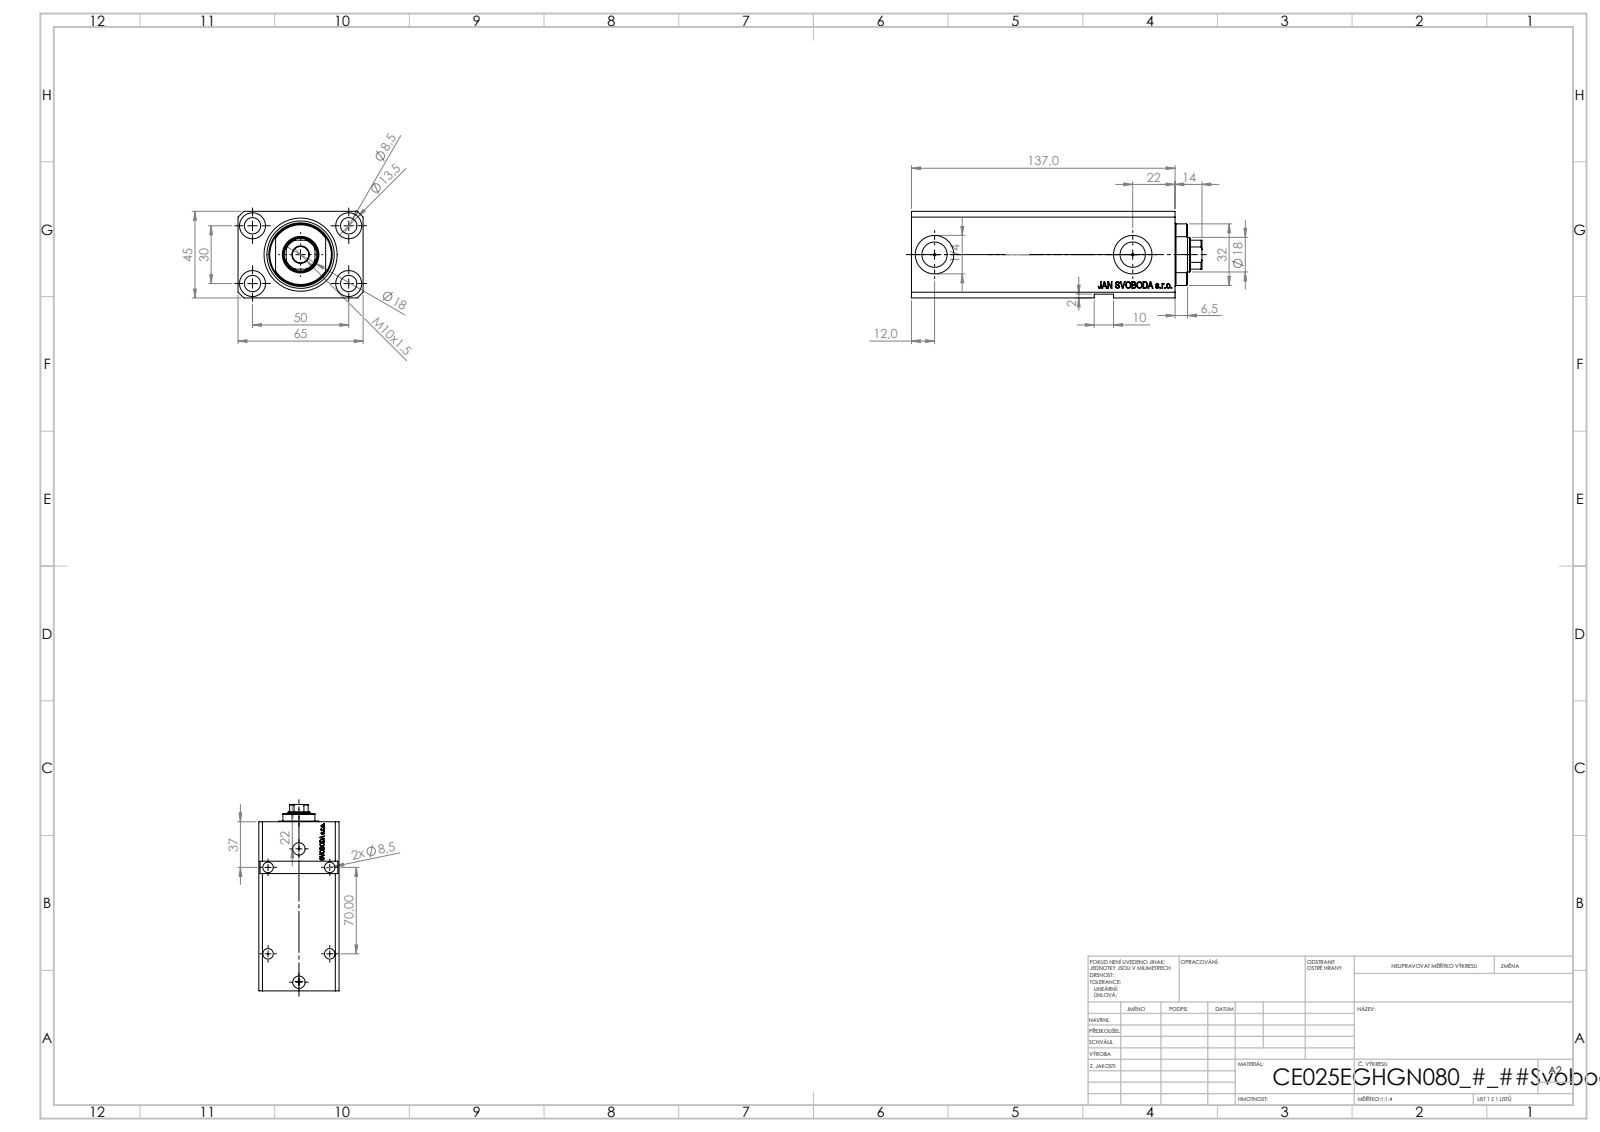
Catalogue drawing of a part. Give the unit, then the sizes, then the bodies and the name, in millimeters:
Units: millimetres
Overall size (bounding box): 151 × 65 × 45
Round holes (diameter × count): ⌀8.5 ×9, ⌀1.25 ×4, ⌀13.5 ×4, ⌀10 ×2, ⌀13.16 ×2, ⌀20 ×2, ⌀18 ×1, ⌀25 ×1, ⌀38 ×1
Partial cylindrical surfaces — rounded edges, fillets, slot ends (radius × count): R8.5 ×1, R16 ×1
Main face-to-face distances: 45, 65, 123, 14, 137, 6.9, 116.1, 130.1, 43, 9
Hole centre spacings: 29.15, 50, 30, 33.61, 33.97, 58.31, 70, 86.02
Volume: 334 862 mm³ · Surface area: 80 572 mm²
Bodies: 3 solids, 917 faces (435 planar, 104 cylindrical, 378 other)
Part name (STEP PRODUCT): V250CE_E_Body; V250CE_C_VCP; V250CE_VC_E
STEP written by: SolidWorks 2019 (CONFIG_CONTROL_DESIGN)
